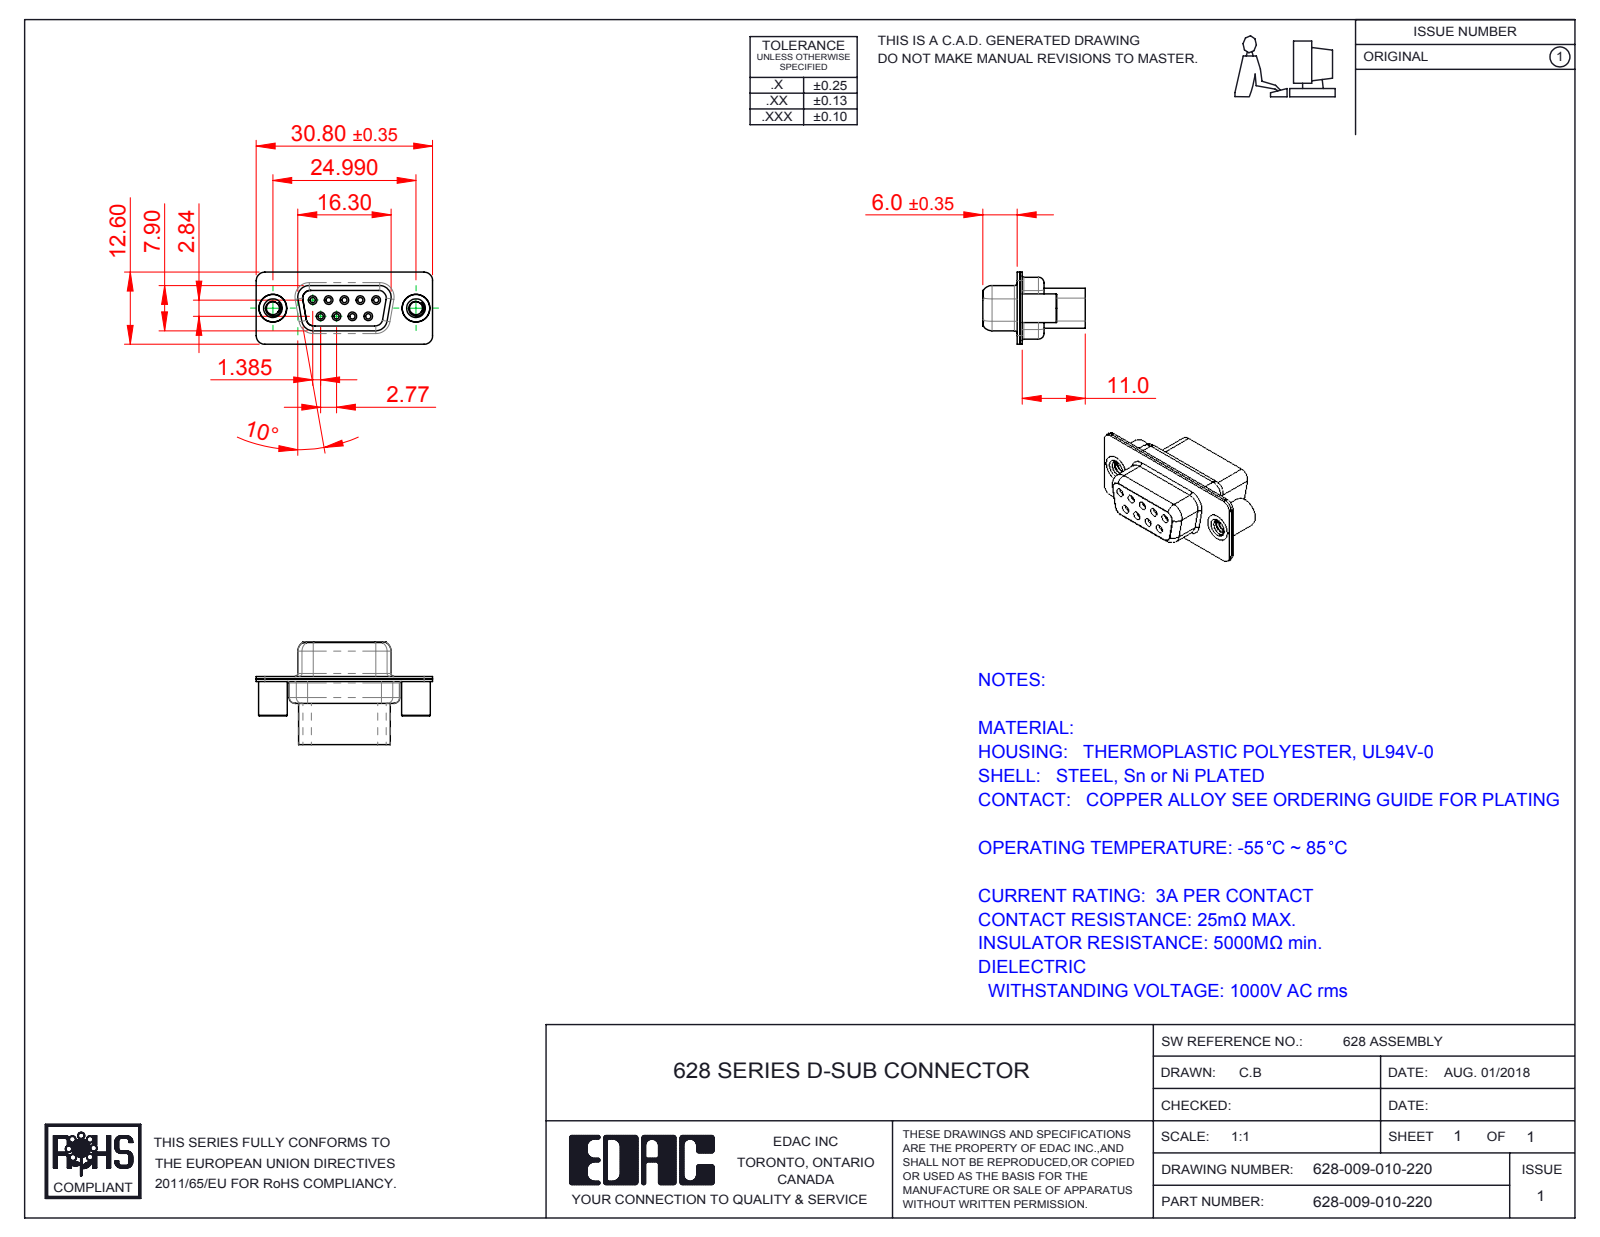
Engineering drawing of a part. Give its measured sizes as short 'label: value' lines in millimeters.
name: 628-009-010-220; 628 Shell Front_09 Contacts; 628 Housing_09 HP; 628 4-40 Threaded Standoff BS (+1 more)
written by: SolidWorks 2016 (CONFIG_CONTROL_DESIGN)
unit: mm
bodies: 5 solids, 418 faces (94 planar, 229 cylindrical, 95 other)
size: 30.8 × 17.9 × 12.6
volume: 2 243 mm³; area: 4 285 mm²
holes: 9× ⌀0.9, 9× ⌀1.5, 9× ⌀2, 5× ⌀1.7, 4× ⌀1.6, 2× ⌀2.26, 2× ⌀4, 2× ⌀4.05, 2× ⌀4.85
bosses: 2× ⌀5, 2× ⌀4.95, 2× ⌀4.8
rounds: 17× R1.5, 12× R2, 6× R1.35, 4× R0.25, 4× R0.5, 4× R0.6, 4× R0.65, 4× R0.95
face distances: 0.45, 0.4, 0.9, 6.6, 1.9, 8.5, 1.4, 7, 0.5, 11.9
hole spacings: 3.16, 2.77, 5.54, 5.03, 5.04, 8.31, 7.48, 7.49
